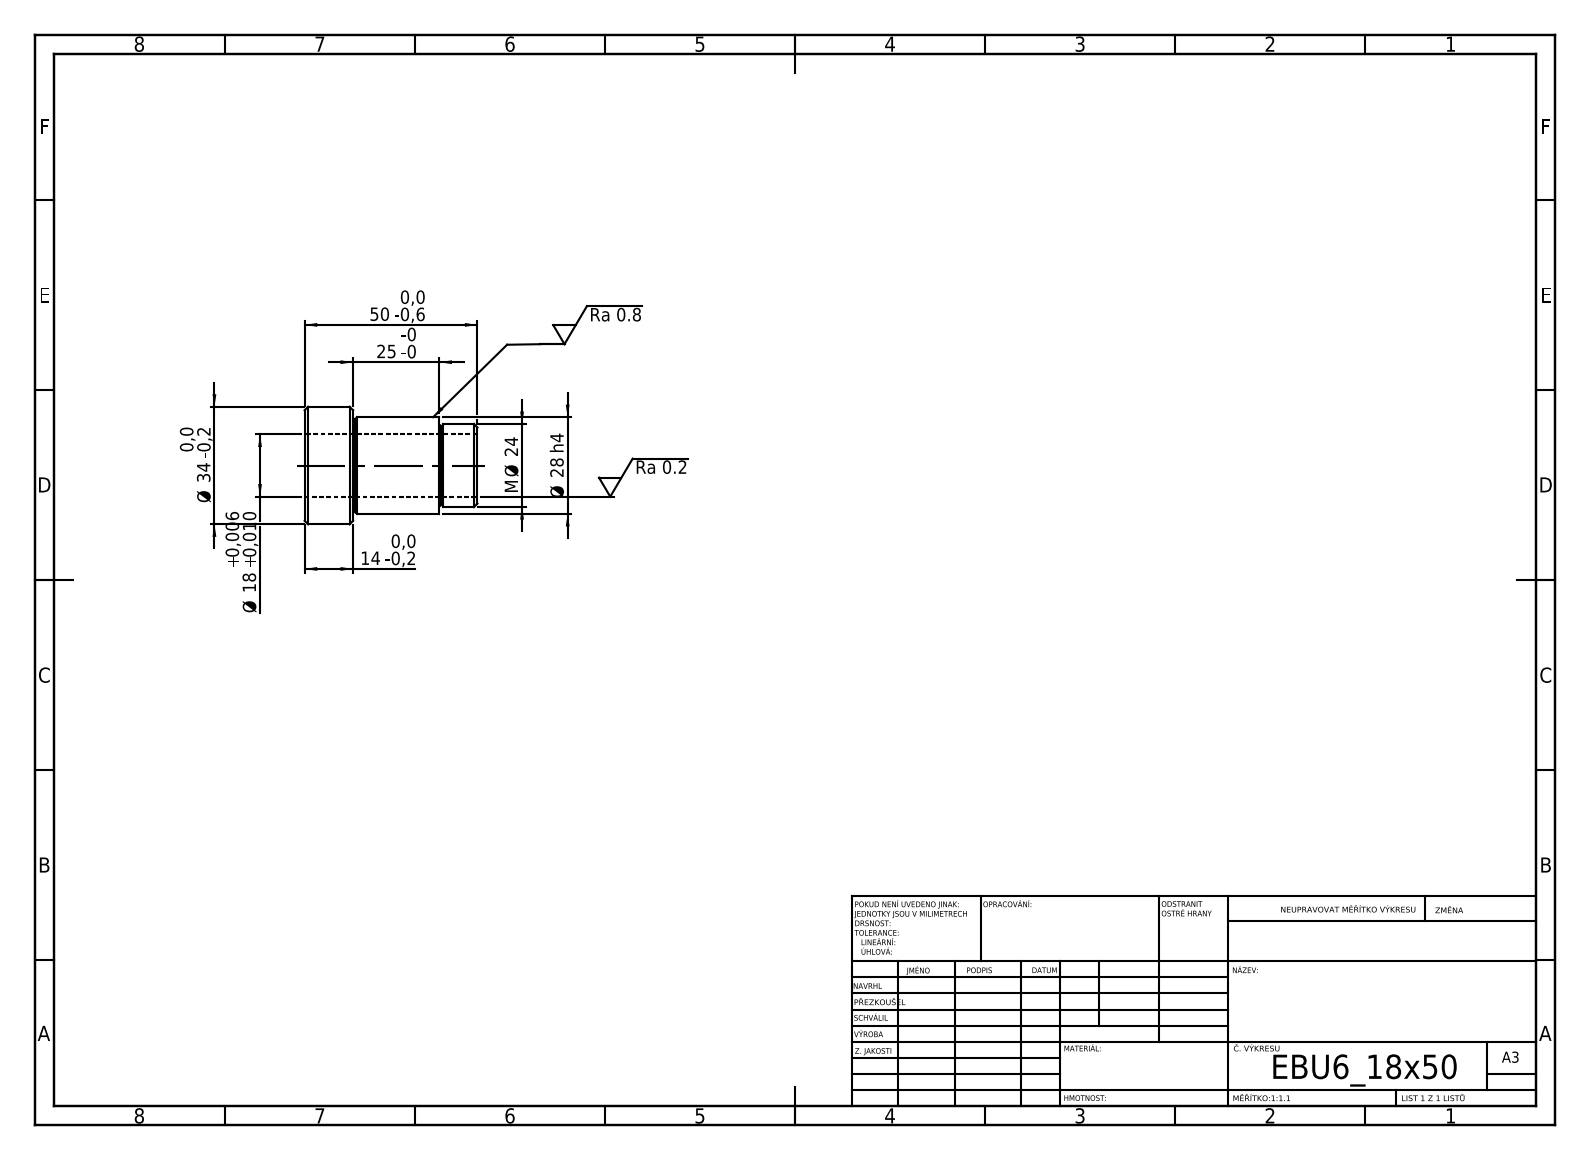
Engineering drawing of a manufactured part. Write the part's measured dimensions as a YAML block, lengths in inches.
step_written_by: "SolidWorks 2019 (CONFIG_CONTROL_DESIGN)"
units: inches
bodies: {solids: 1, faces: 27, planar: 5, cylindrical: 12, other: 10}
overall_size: [1.969, 1.339, 1.339]
volume: 1.229
surface_area: 13.34
round_holes:
  - {diameter: 0.709, count: 1}
round_bosses_or_shafts:
  - {diameter: 1.339, count: 1}
  - {diameter: 1.102, count: 1}
  - {diameter: 1.063, count: 1}
  - {diameter: 0.945, count: 1}
  - {diameter: 0.906, count: 1}
face_to_face_distances: [0.551, 0.984, 1.535, 0.433, 1.417, 1.969, 0.394, 0.039, 1.024, 1.575]
